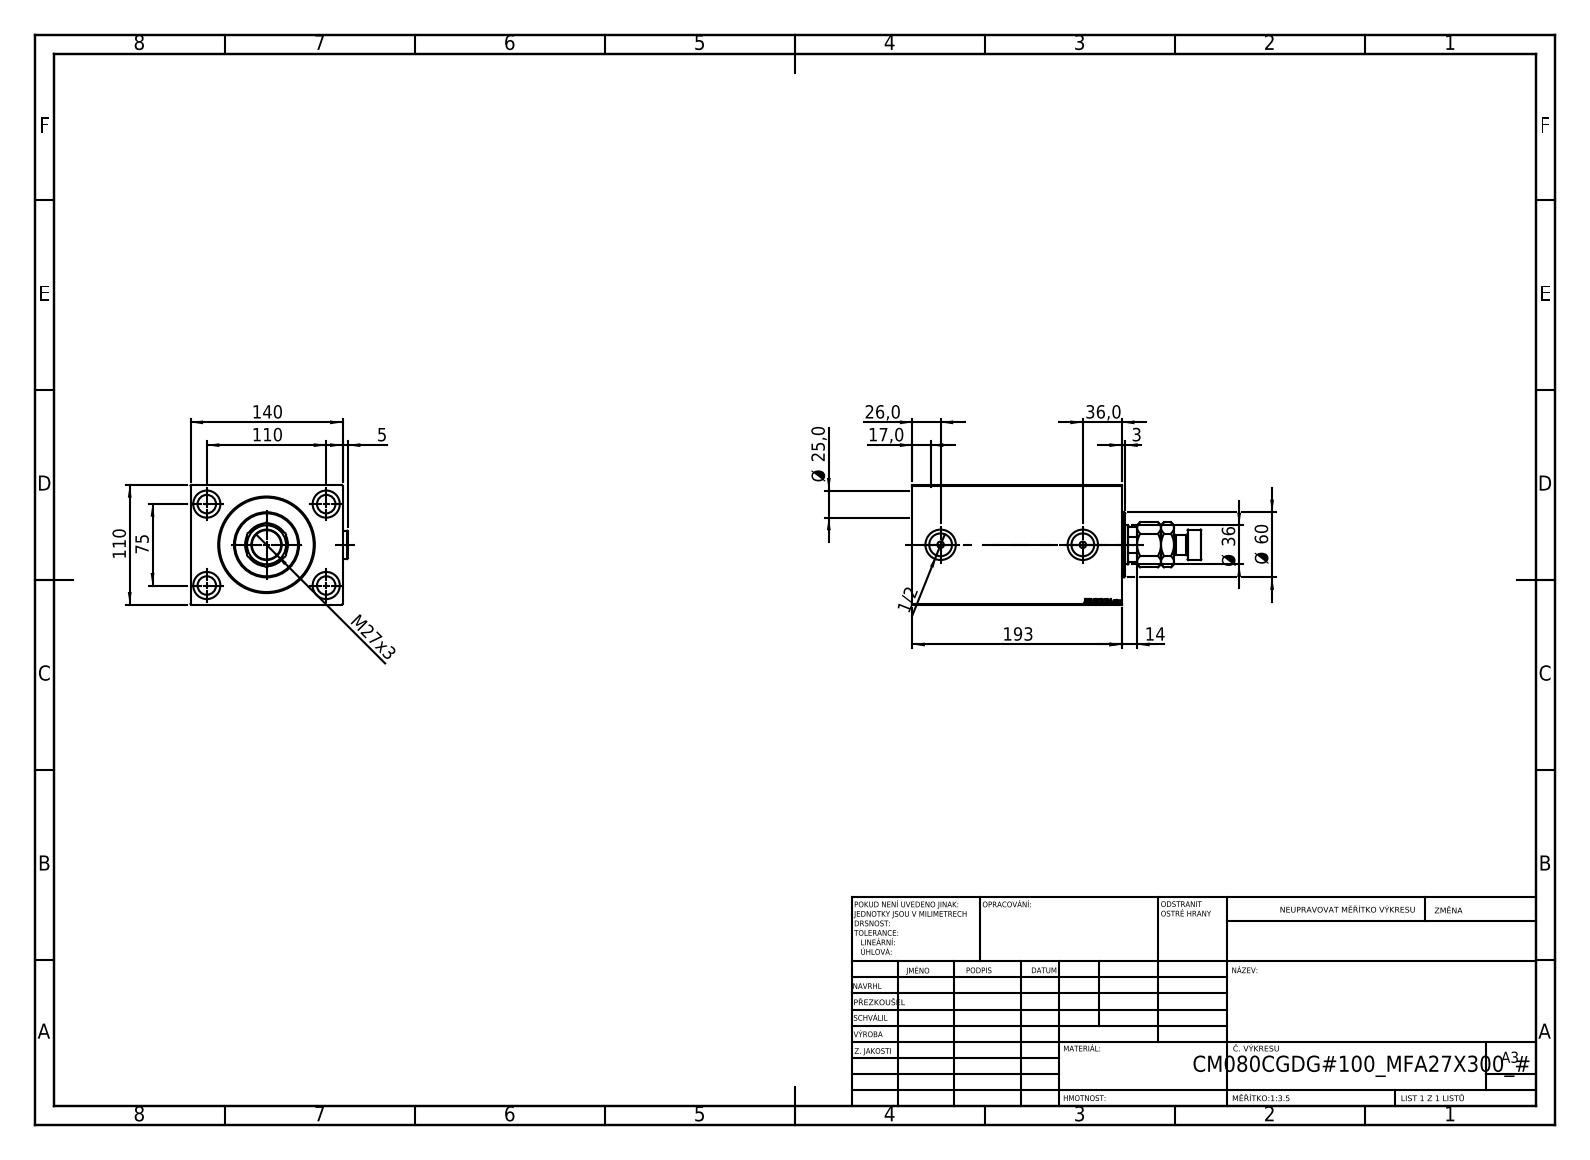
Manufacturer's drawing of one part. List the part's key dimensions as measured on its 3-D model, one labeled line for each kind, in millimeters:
Part name (STEP PRODUCT): Zatka_OIL_PORT; V450CM_C_Body; MFA; V450CM_C_VCP (+1 more)
STEP written by: SolidWorks 2019 (CONFIG_CONTROL_DESIGN)
Units: millimetres
Bodies: 6 solids, 971 faces (459 planar, 82 cylindrical, 430 other)
Overall size (bounding box): 266 × 144.9 × 110
Volume: 2 394 000 mm³ · Surface area: 287 252 mm²
Round holes (diameter × count): ⌀17 ×4, ⌀25 ×4, ⌀6 ×2, ⌀20.96 ×2, ⌀28 ×2, ⌀25.5 ×1, ⌀36 ×1, ⌀39.5 ×1, ⌀80 ×1, ⌀82 ×1, ⌀87 ×1
Round bosses / shafts (diameter × count): ⌀26 ×2, ⌀60 ×1, ⌀28 ×1, ⌀18 ×1
Partial cylindrical surfaces — rounded edges, fillets, slot ends (radius × count): R17.5 ×1
Main face-to-face distances: 110, 140, 193, 172, 21, 14, 179, 158, 100, 114
Hole centre spacings: 66.57, 75, 110, 133.14, 131
